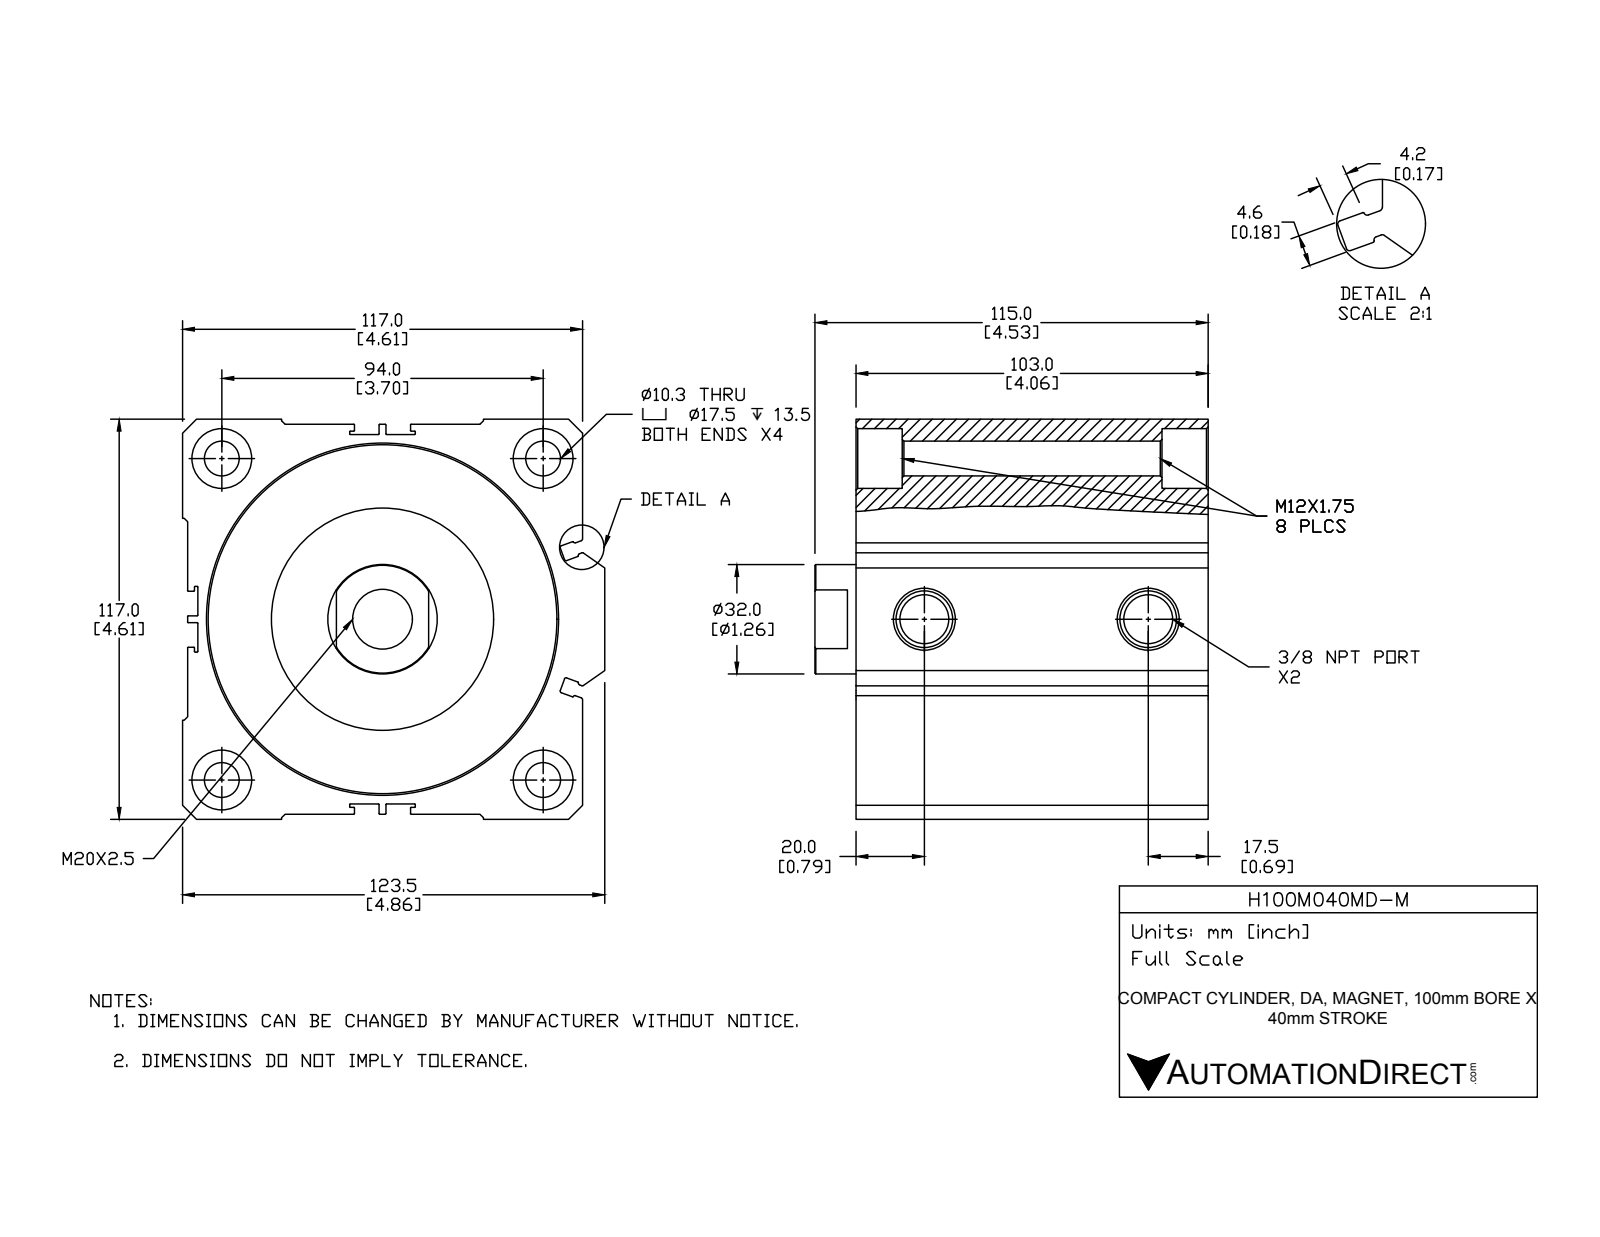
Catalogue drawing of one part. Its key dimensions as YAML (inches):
part_name: "H100M040MD-M-BODY; H100M040MD-M-PISTON; H100M040MD-M"
step_written_by: "SolidWorks 2015 (CONFIG_CONTROL_DESIGN)"
units: inches
bodies: {solids: 2, faces: 261, planar: 105, cylindrical: 103, other: 53}
overall_size: [4.862, 4.606, 4.528]
volume: 59.7
surface_area: 272.7
round_holes:
  - {diameter: 0.689, count: 5}
  - {diameter: 0.402, count: 4}
  - {diameter: 0.562, count: 2}
  - {diameter: 1.26, count: 1}
  - {diameter: 2.559, count: 1}
  - {diameter: 3.937, count: 1}
  - {diameter: 4.016, count: 1}
round_bosses_or_shafts:
  - {diameter: 1.535, count: 1}
partial_cylinders:
  - {radius: 0.008, count: 40}
  - {radius: 0.02, count: 12}
face_to_face_distances: [0.059, 4.547, 4.606, 2.697, 1.094, 1.602, 0.492, 1.587, 3.189, 0.079]
hole_center_spacings: [2.617, 3.701, 5.234, 2.579]
